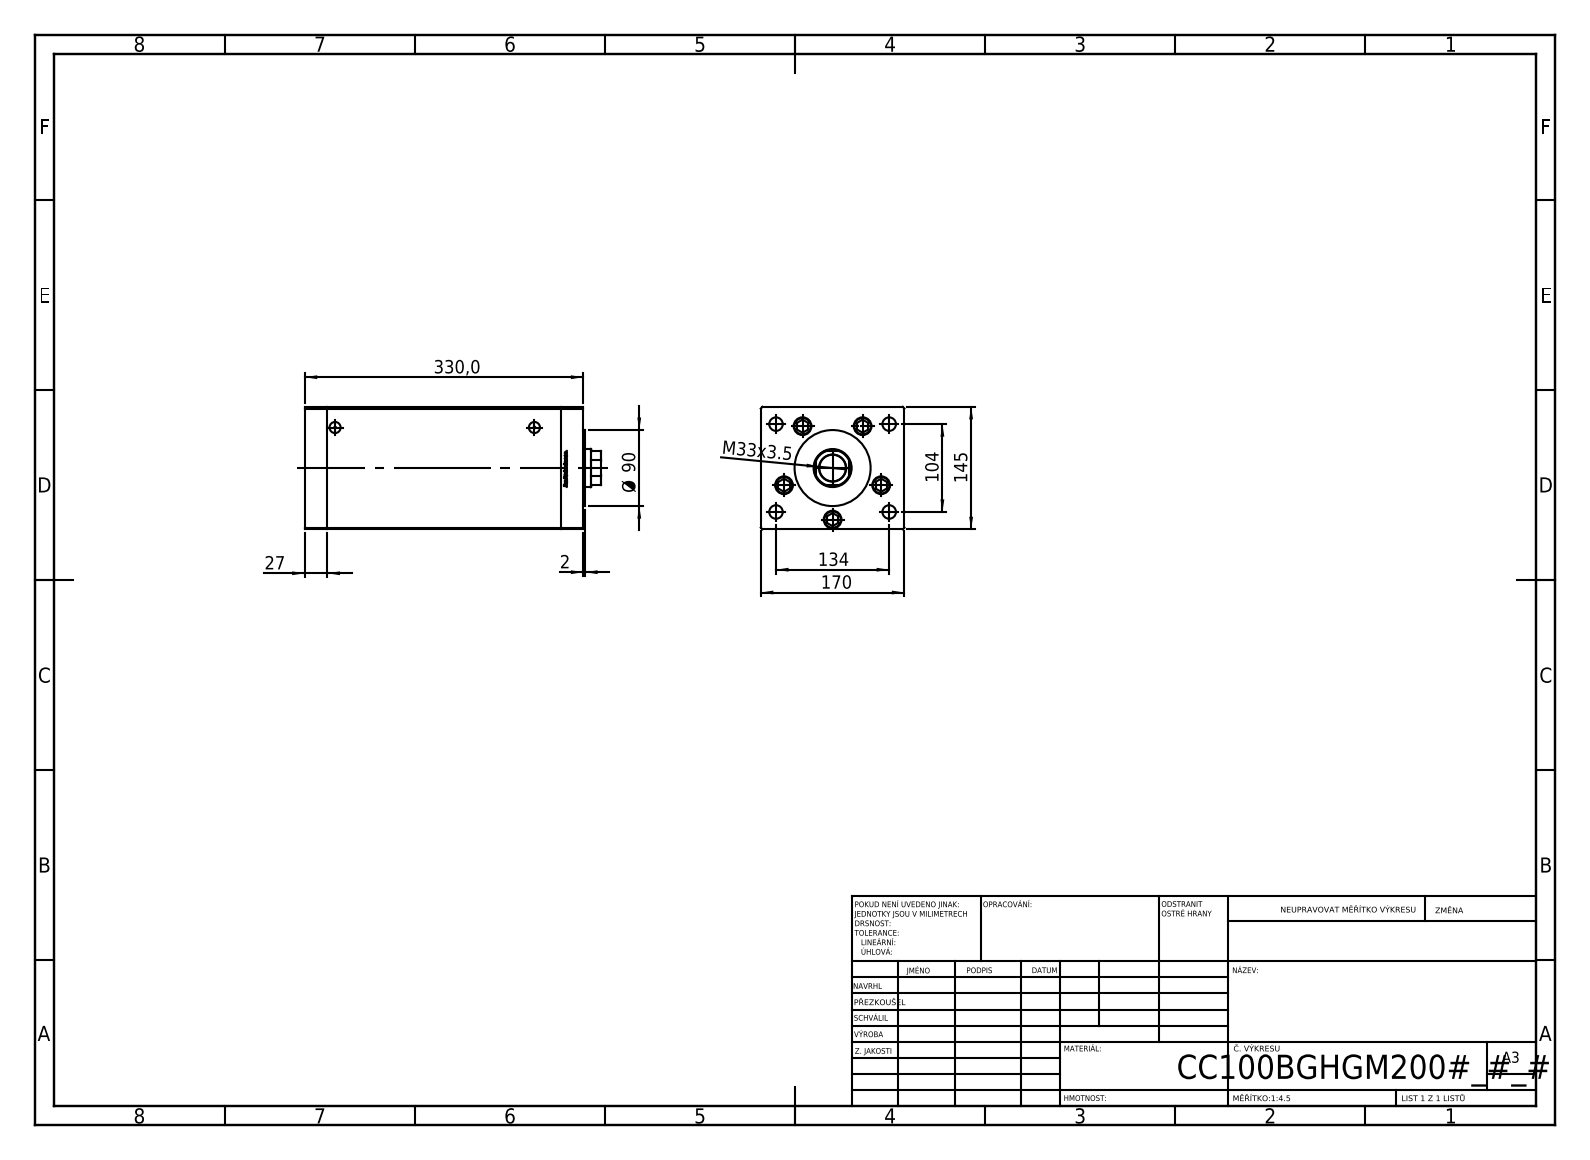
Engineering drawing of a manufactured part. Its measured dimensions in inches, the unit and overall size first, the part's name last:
Units: inches
Overall size (bounding box): 13.819 × 6.693 × 5.709
Round holes (diameter × count): ⌀0.689 ×5, ⌀0.827 ×5, ⌀0.63 ×4, ⌀0.079 ×2, ⌀0.518 ×2, ⌀1.24 ×1, ⌀1.772 ×1
Round bosses / shafts (diameter × count): ⌀0.315 ×5, ⌀3.937 ×1, ⌀3.543 ×1
Partial cylindrical surfaces — rounded edges, fillets, slot ends (radius × count): R0.037 ×2, R0.866 ×1
Main face-to-face distances: 5.709, 6.693, 1.063, 11.929, 10.866, 1.496, 0.433, 12.992, 10.433, 11.496
Hole centre spacings: 2.402, 3.339, 1.241, 1.302, 2.661, 2.773, 2.872, 2.884
Volume: 408.7 in³ · Surface area: 876.9 in²
Bodies: 14 solids, 1185 faces (464 planar, 147 cylindrical, 574 other)
Part name (STEP PRODUCT): V220C_VC_B; V220C_B MIDDLE; ALLEN BOLT; V220C BACK_B (+1 more)
STEP written by: SolidWorks 2019 (CONFIG_CONTROL_DESIGN)
